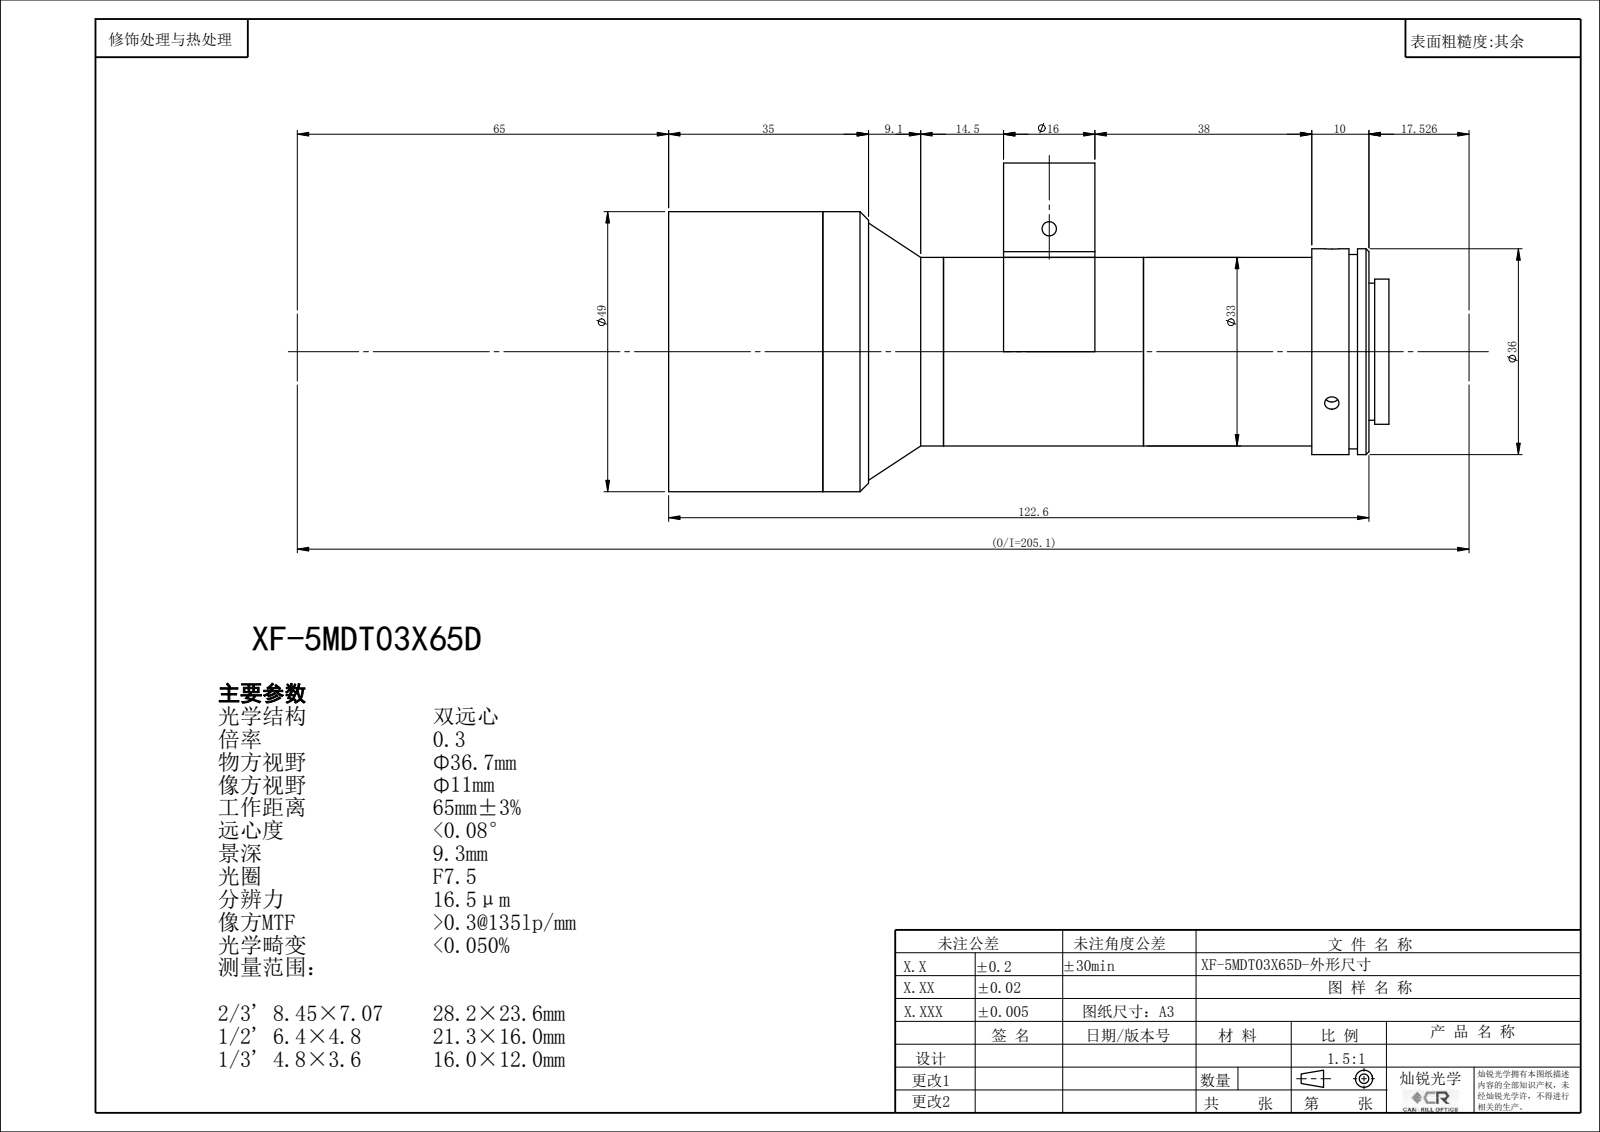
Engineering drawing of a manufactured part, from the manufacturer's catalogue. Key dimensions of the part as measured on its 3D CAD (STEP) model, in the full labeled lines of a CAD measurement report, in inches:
Part name (STEP PRODUCT): XF-5MDT03X65D
STEP written by: SolidWorks 2014 (CONFIG_CONTROL_DESIGN)
Units: inches
Bodies: 0 solids, 115 faces (38 planar, 65 cylindrical, 12 other)
Overall size (bounding box): 4.965 × 2.264 × 1.929
Round holes (diameter × count): ⌀0.098 ×8, ⌀0.138 ×4, ⌀0.551 ×1, ⌀0.63 ×1, ⌀0.89 ×1, ⌀1.654 ×1, ⌀1.772 ×1
Round bosses / shafts (diameter × count): ⌀1.929 ×1, ⌀1.417 ×1, ⌀1.339 ×1, ⌀1.299 ×1, ⌀1.102 ×1, ⌀1 ×1, ⌀0.945 ×1, ⌀0.63 ×1
Main face-to-face distances: 3.764, 3.37, 0.256, 0.039, 1.063, 4.827, 1.299, 0.019, 1.044, 4.807
Hole centre spacings: 0.592, 0.433, 1.102, 1.184, 1.817, 2.233, 1.948
